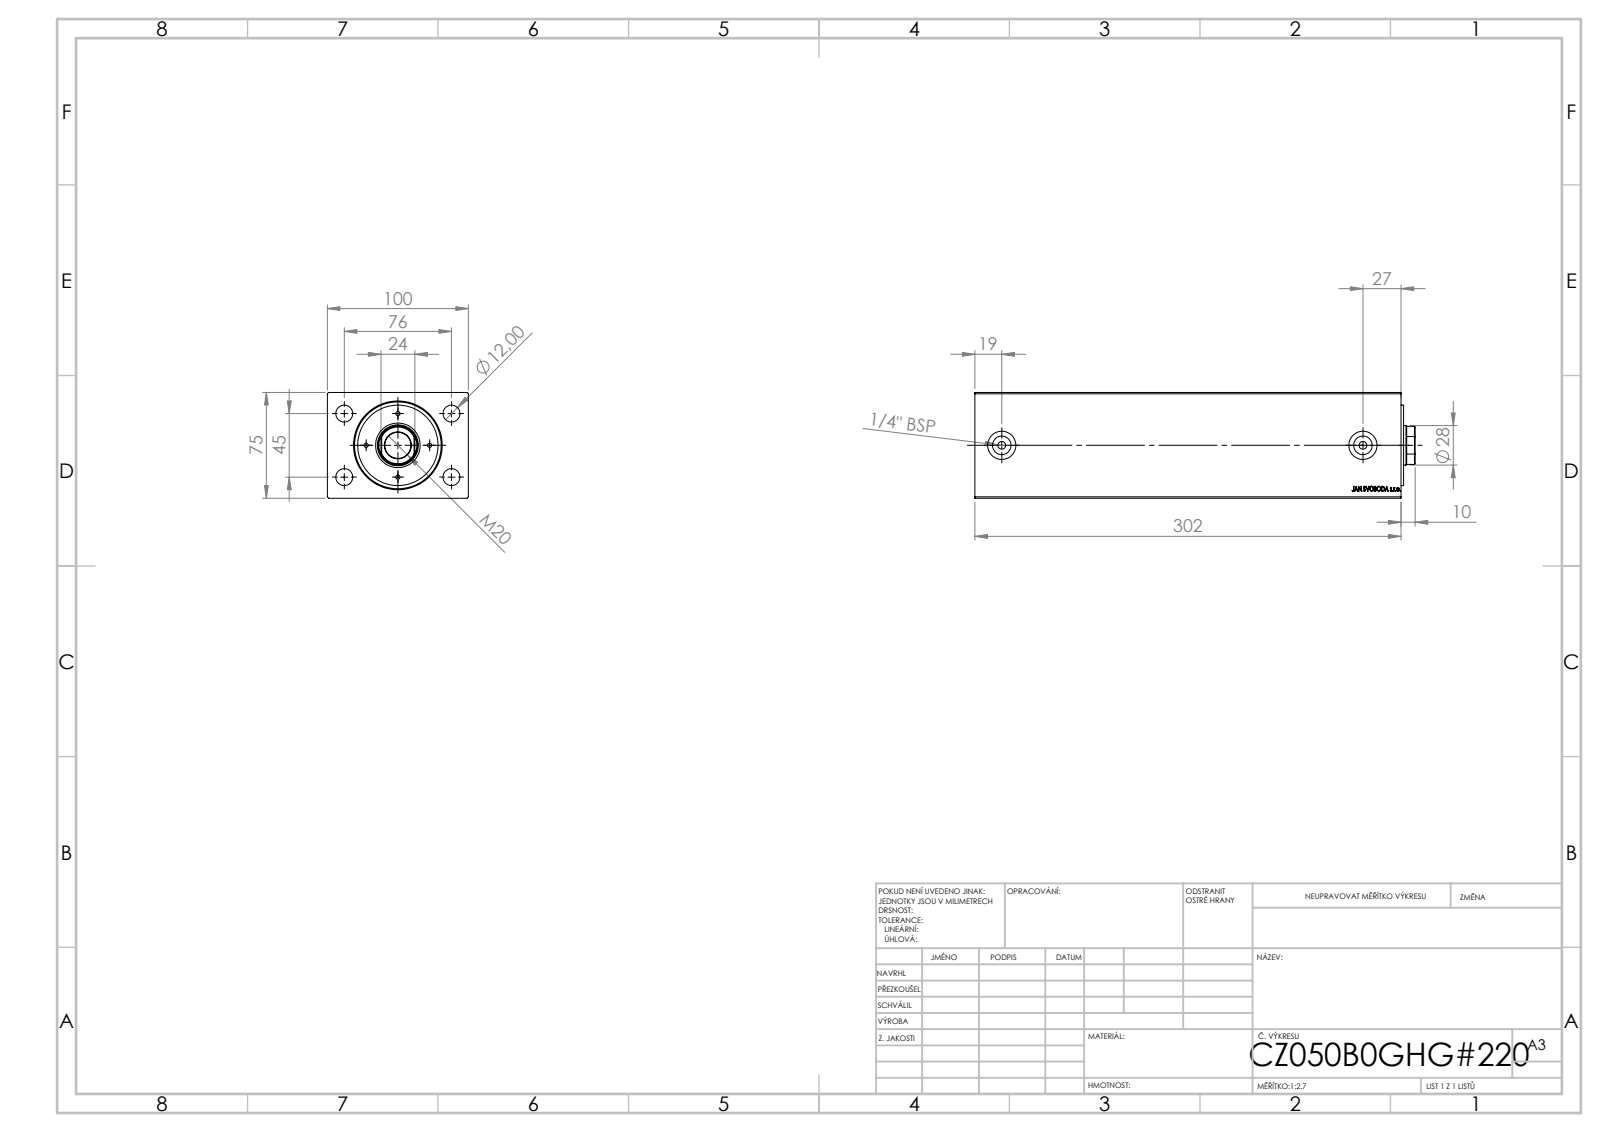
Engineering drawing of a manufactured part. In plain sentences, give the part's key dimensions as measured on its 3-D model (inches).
The part is named "V500CZ_B_VC; V500CZ". Its 3-D file was written by "SolidWorks 2019 (CONFIG_CONTROL_DESIGN)". It is 3 solids with 873 faces: 399 planar, 58 cylindrical and 416 other. Overall it measures 12.283 by 3.937 by 2.953 inches. Its volume is 122.7 cubic inches and its surface area 369.7 square inches. Round holes: 4 of diameter 0.118, 4 of diameter 0.472, 2 of diameter 0.217, 2 of diameter 0.518, 2 of diameter 0.787, 1 of diameter 0.728, 1 of diameter 1.102, 1 of diameter 1.142, 1 of diameter 1.417, 1 of diameter 1.969, 1 of diameter 2.421. Round bosses or shafts: 1 of diameter 2.244. Partial cylindrical surfaces (rounded edges, fillets, slot ends): 1 of radius 0.531. The main face-to-face distances are 2.953, 3.937, 11.89, 11.201, 0.689, 3.228, 7.972, 8.661, 0.071, 3.299. The hole center spacings are 0.886, 1.076, 1.253, 1.496, 1.739, 1.772, 2.319, 2.541.
